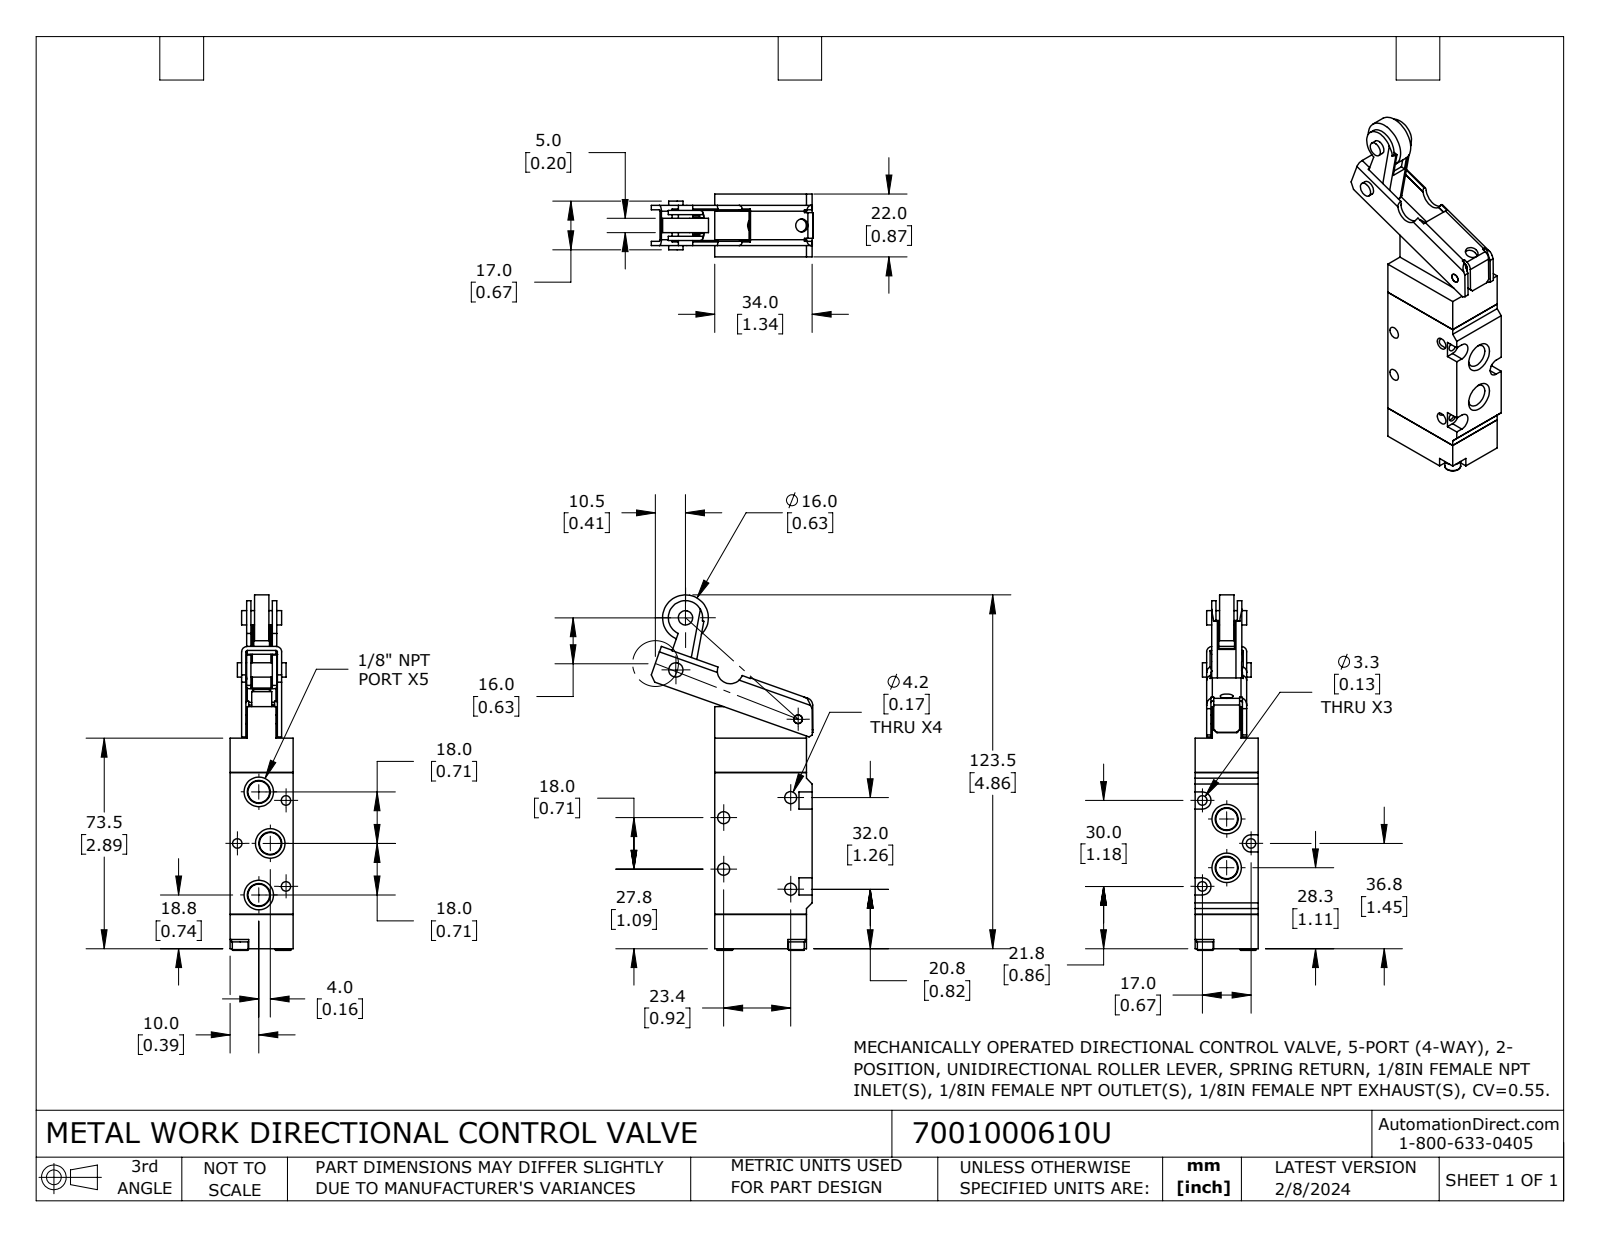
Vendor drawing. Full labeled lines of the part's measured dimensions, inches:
Part name (STEP PRODUCT): 7001000610U
STEP written by: SolidWorks 2023 (CONFIG_CONTROL_DESIGN)
Units: inches
Bodies: 9 solids, 278 faces (137 planar, 91 cylindrical, 50 other)
Overall size (bounding box): 4.886 × 2.223 × 0.866
Volume: 3.548 in³ · Surface area: 35.84 in²
Round holes (diameter × count): ⌀0.165 ×4, ⌀0.118 ×3, ⌀0.13 ×3, ⌀0.177 ×1
Round bosses / shafts (diameter × count): ⌀0.236 ×2, ⌀0.217 ×2, ⌀0.197 ×2, ⌀0.63 ×1, ⌀0.276 ×1
Partial cylindrical surfaces — rounded edges, fillets, slot ends (radius × count): R0.02 ×4, R0.079 ×4, R0.118 ×3, R0.039 ×1, R0.098 ×1, R0.177 ×1, R0.217 ×1, R0.236 ×1
Main face-to-face distances: 0.866, 0.059, 0.472, 0.079, 1.949, 0.157, 0.709, 0.217, 0.65, 0.492
Hole centre spacings: 0.893, 0.961, 1.348, 0.709, 1.081, 1.148, 1.181, 1.26
